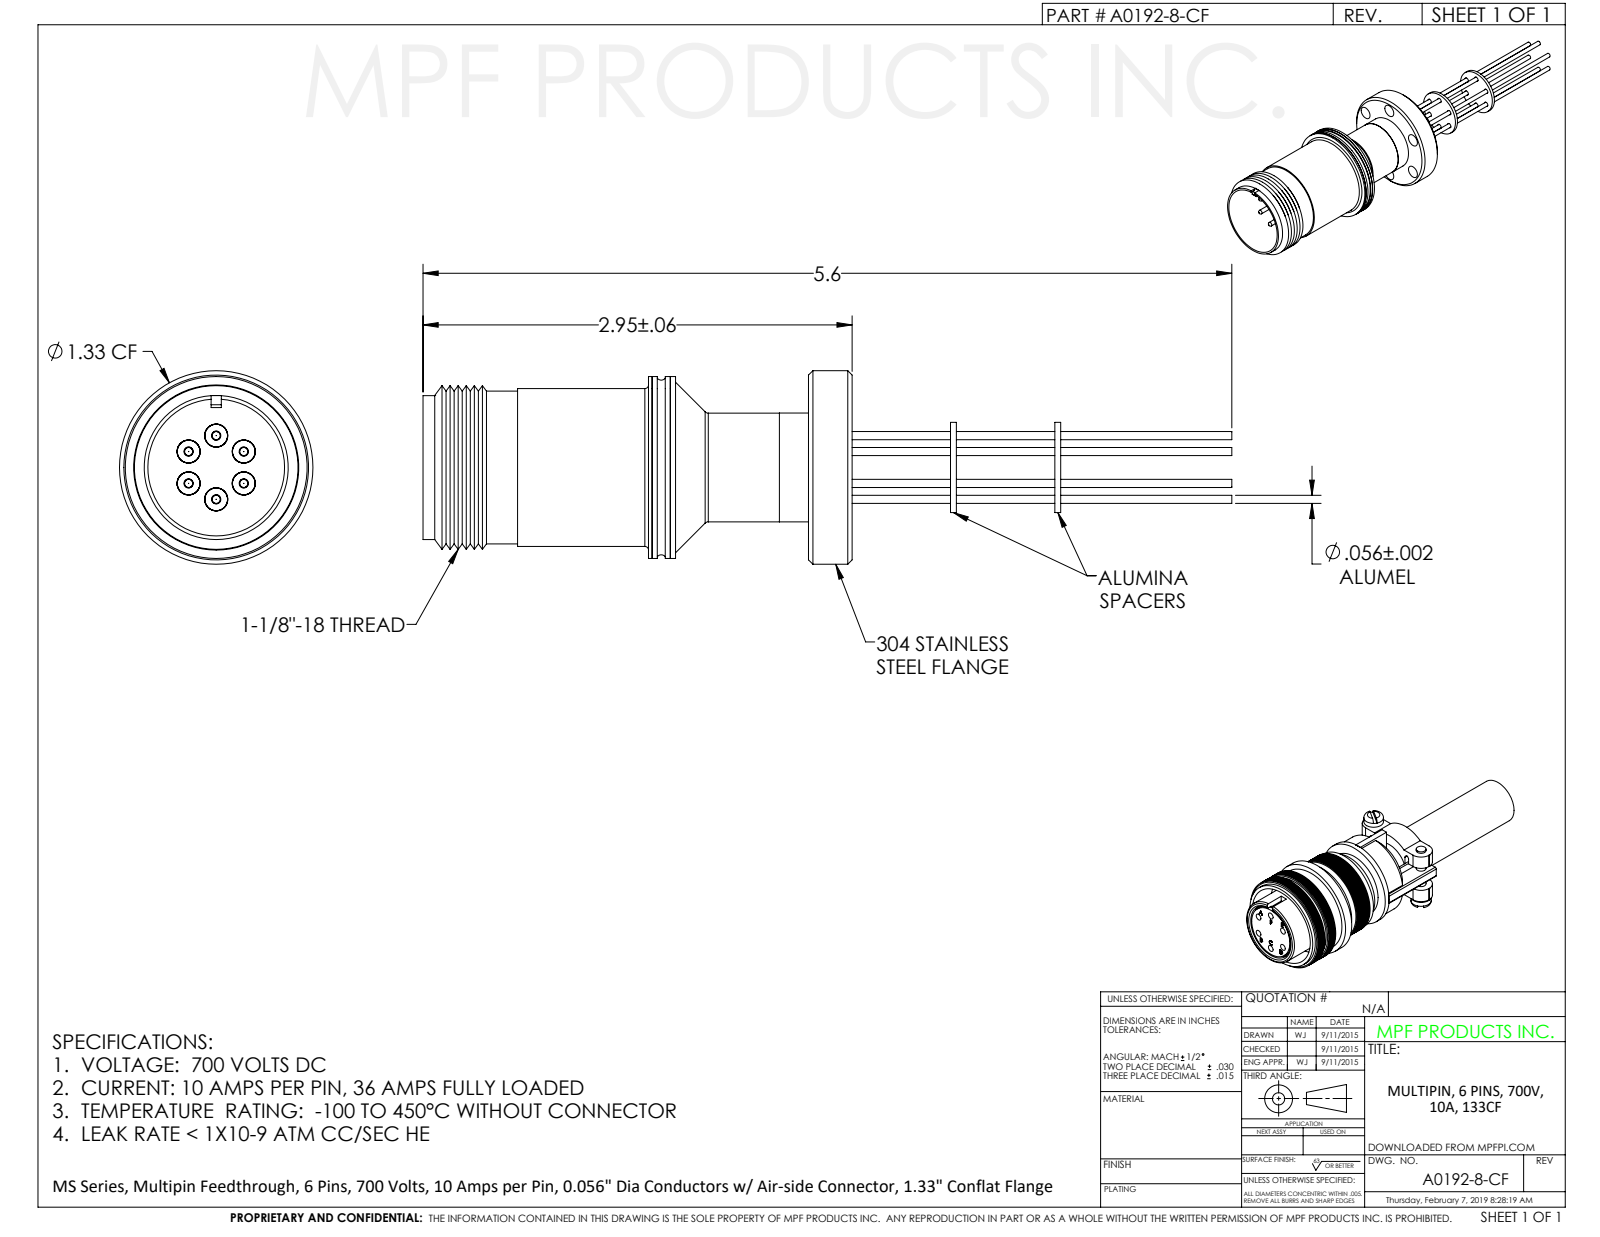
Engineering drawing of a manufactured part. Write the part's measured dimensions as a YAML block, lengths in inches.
part_name: "A0192-8-CF"
step_written_by: "SolidWorks 2012 (CONFIG_CONTROL_DESIGN)"
units: inches
bodies: {solids: 1, faces: 261, planar: 63, cylindrical: 136, other: 62}
overall_size: [5.595, 1.33, 1.33]
volume: 0.941
surface_area: 34.69
round_holes:
  - {diameter: 0.172, count: 6}
  - {diameter: 0.63, count: 1}
  - {diameter: 0.675, count: 1}
  - {diameter: 0.725, count: 1}
  - {diameter: 0.845, count: 1}
  - {diameter: 0.94, count: 1}
  - {diameter: 0.97, count: 1}
  - {diameter: 1.035, count: 1}
round_bosses_or_shafts:
  - {diameter: 0.187, count: 6}
  - {diameter: 0.17, count: 6}
  - {diameter: 0.056, count: 6}
  - {diameter: 1.33, count: 1}
  - {diameter: 1.25, count: 1}
  - {diameter: 1.085, count: 1}
  - {diameter: 1.05, count: 1}
  - {diameter: 1.02, count: 1}
face_to_face_distances: [1.52, 1.805, 0.285, 0.05, 1.47, 1.755, 0.15, 0.04, 2.479, 3.223]
hole_center_spacings: [0.531, 0.92, 0.531, 1.062, 1.062]
